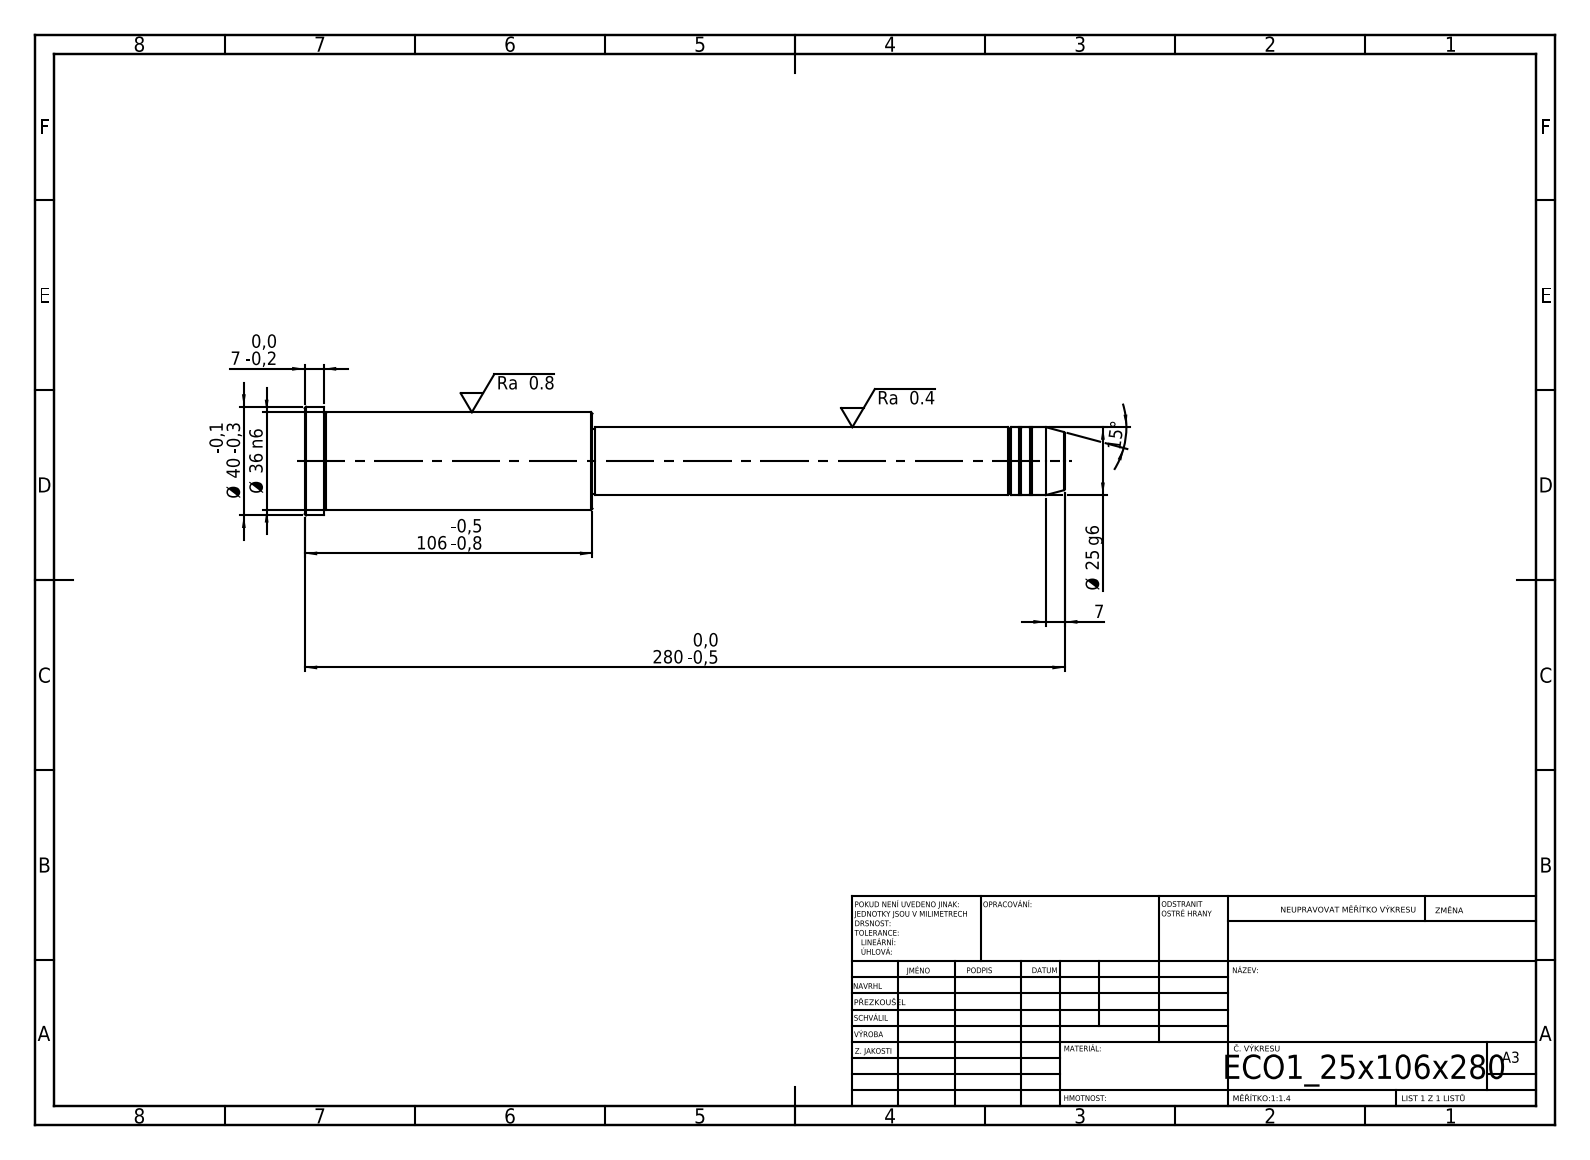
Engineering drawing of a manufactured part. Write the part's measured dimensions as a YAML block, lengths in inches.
step_written_by: "SolidWorks 2019 (CONFIG_CONTROL_DESIGN)"
units: inches
bodies: {solids: 1, faces: 43, planar: 5, cylindrical: 14, other: 24}
overall_size: [11.024, 1.575, 1.575]
volume: 11.86
surface_area: 43.83
round_bosses_or_shafts:
  - {diameter: 1.575, count: 1}
  - {diameter: 1.417, count: 1}
  - {diameter: 0.984, count: 1}
  - {diameter: 0.945, count: 1}
face_to_face_distances: [4.173, 6.85, 11.024, 10.748, 3.898, 0.276, 6.811, 0.039, 3.937, 4.213]
